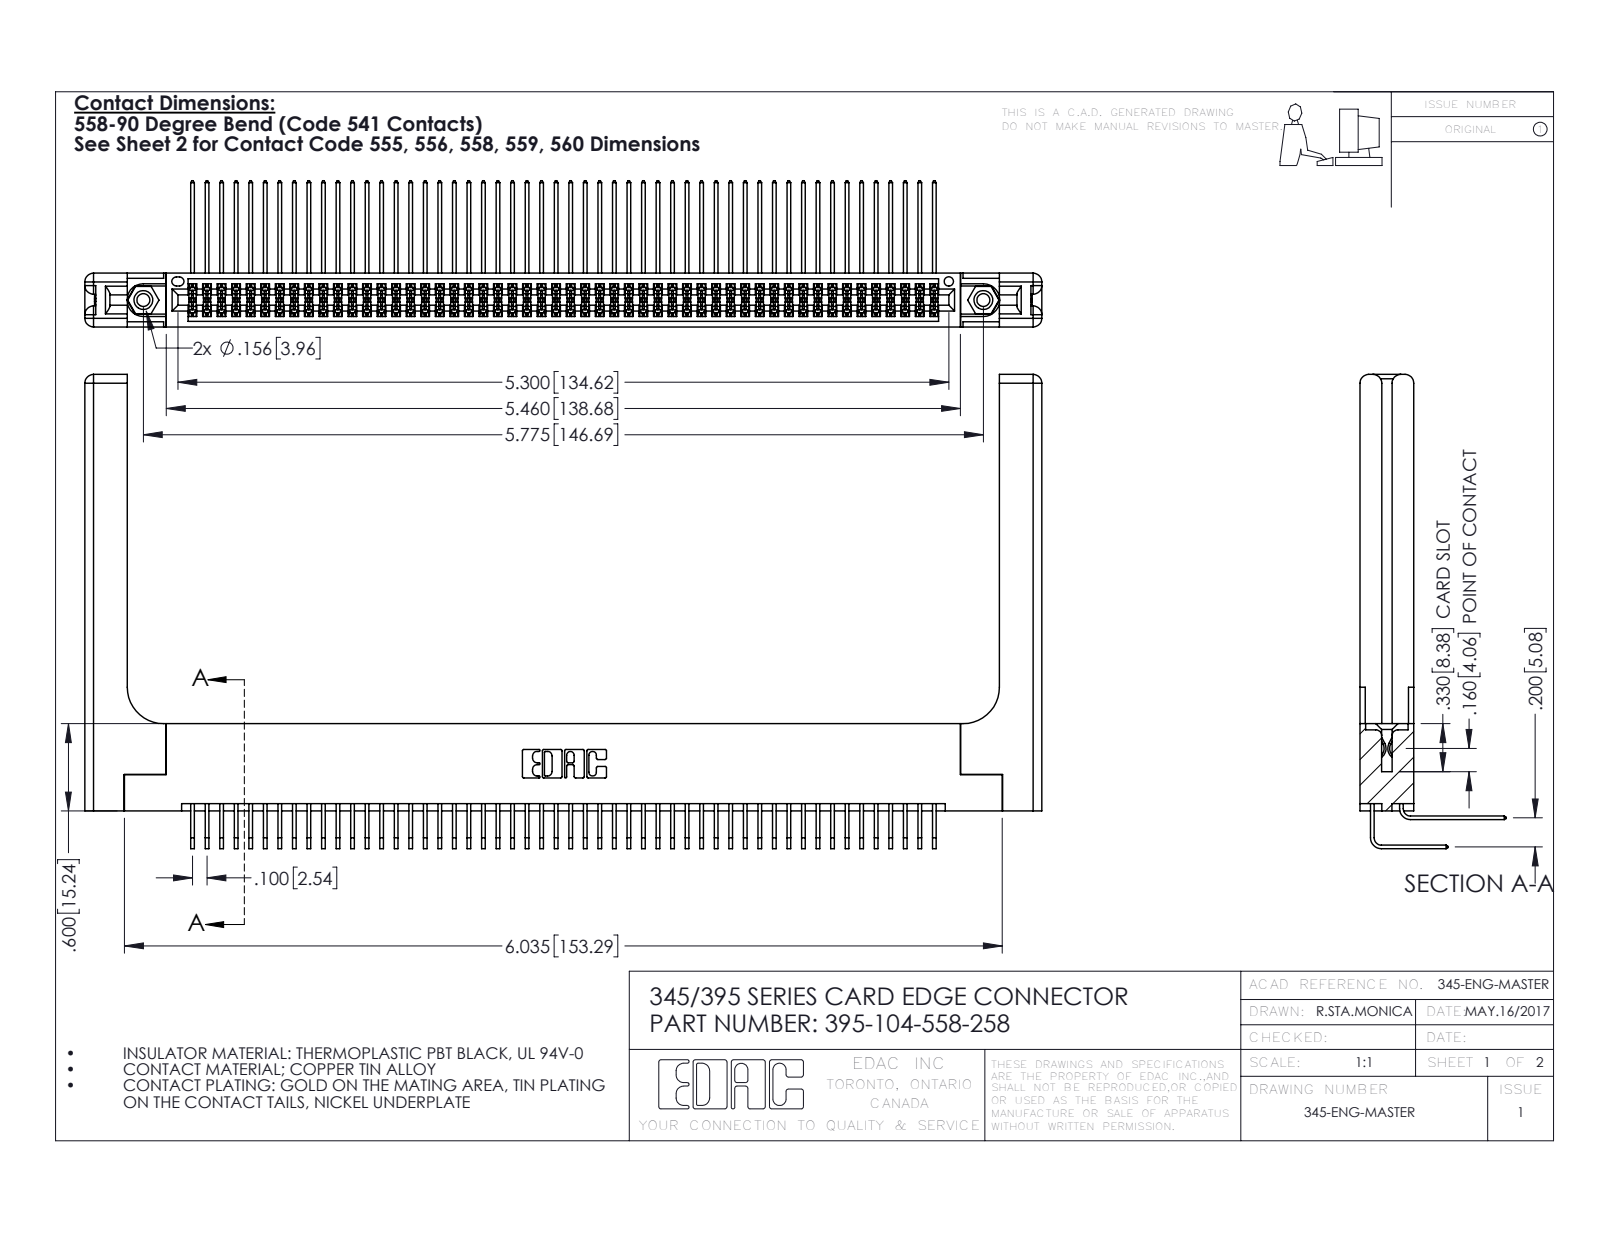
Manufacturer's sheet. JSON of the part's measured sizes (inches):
{"part_name": "345-292-001_558 559 Tail - 1; 395-104-558-258; 345-250-001_345-250-001-102; 345-220-058_345-220-058 (+2 more)", "step_written_by": "SolidWorks 2016 (CONFIG_CONTROL_DESIGN)", "units": "inches", "bodies": {"solids": 109, "faces": 5790, "planar": 3868, "cylindrical": 1862, "other": 60}, "overall_size": [6.579, 3.259, 1.005], "volume_in3": 1.55, "surface_area_in2": 51.29, "round_holes": [[0.089, 2], [0.125, 2], [0.156, 2], [0.064, 1]], "round_bosses_or_shafts": [[0.155, 2]], "partial_cylinders_radius": [[0.006, 157], [0.01, 22], [0.06, 16], [0.007, 6], [0.031, 6], [0.026, 3], [0.014, 2], [0.019, 2]], "face_to_face_distances": [0.072, 0.298, 0.37, 0.2, 0.098, 0.272, 0.025, 0.225, 0.148, 0.15], "hole_center_spacings": [0.27, 5.539, 5.775]}
